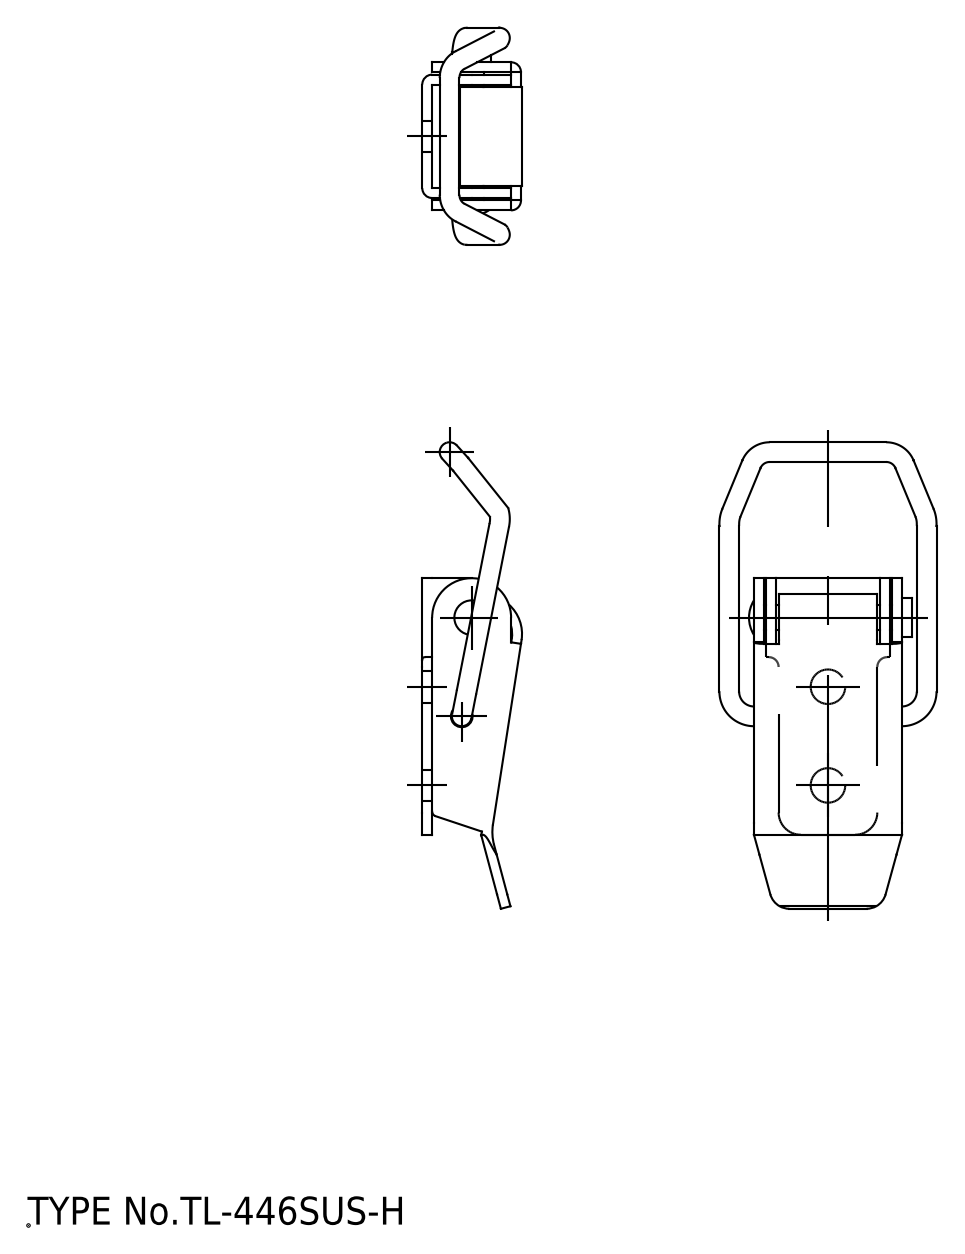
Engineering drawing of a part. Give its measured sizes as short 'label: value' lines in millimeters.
name: ベース; レバー; アーム
written by: spGate 19.8.4 (****-****-****-****) (AUTOMOTIVE_DESIGN)
unit: mm
bodies: 3 solids, 107 faces (41 planar, 49 cylindrical, 17 other)
size: 47.28 × 22 × 10.11
volume: 1 493 mm³; area: 3 234 mm²
holes: 3× ⌀3.5, 1× ⌀2.2
bosses: 5× ⌀2, 1× ⌀4, 1× ⌀2.5
rounds: 8× R1, 2× R2, 2× R2.25, 2× R4, 1× R0.5, 1× R3, 1× R5
face distances: 1, 14, 1.25, 12.75, 15, 13, 11.5, 13.75, 2.25, 11.75
hole spacings: 10, 10.05
